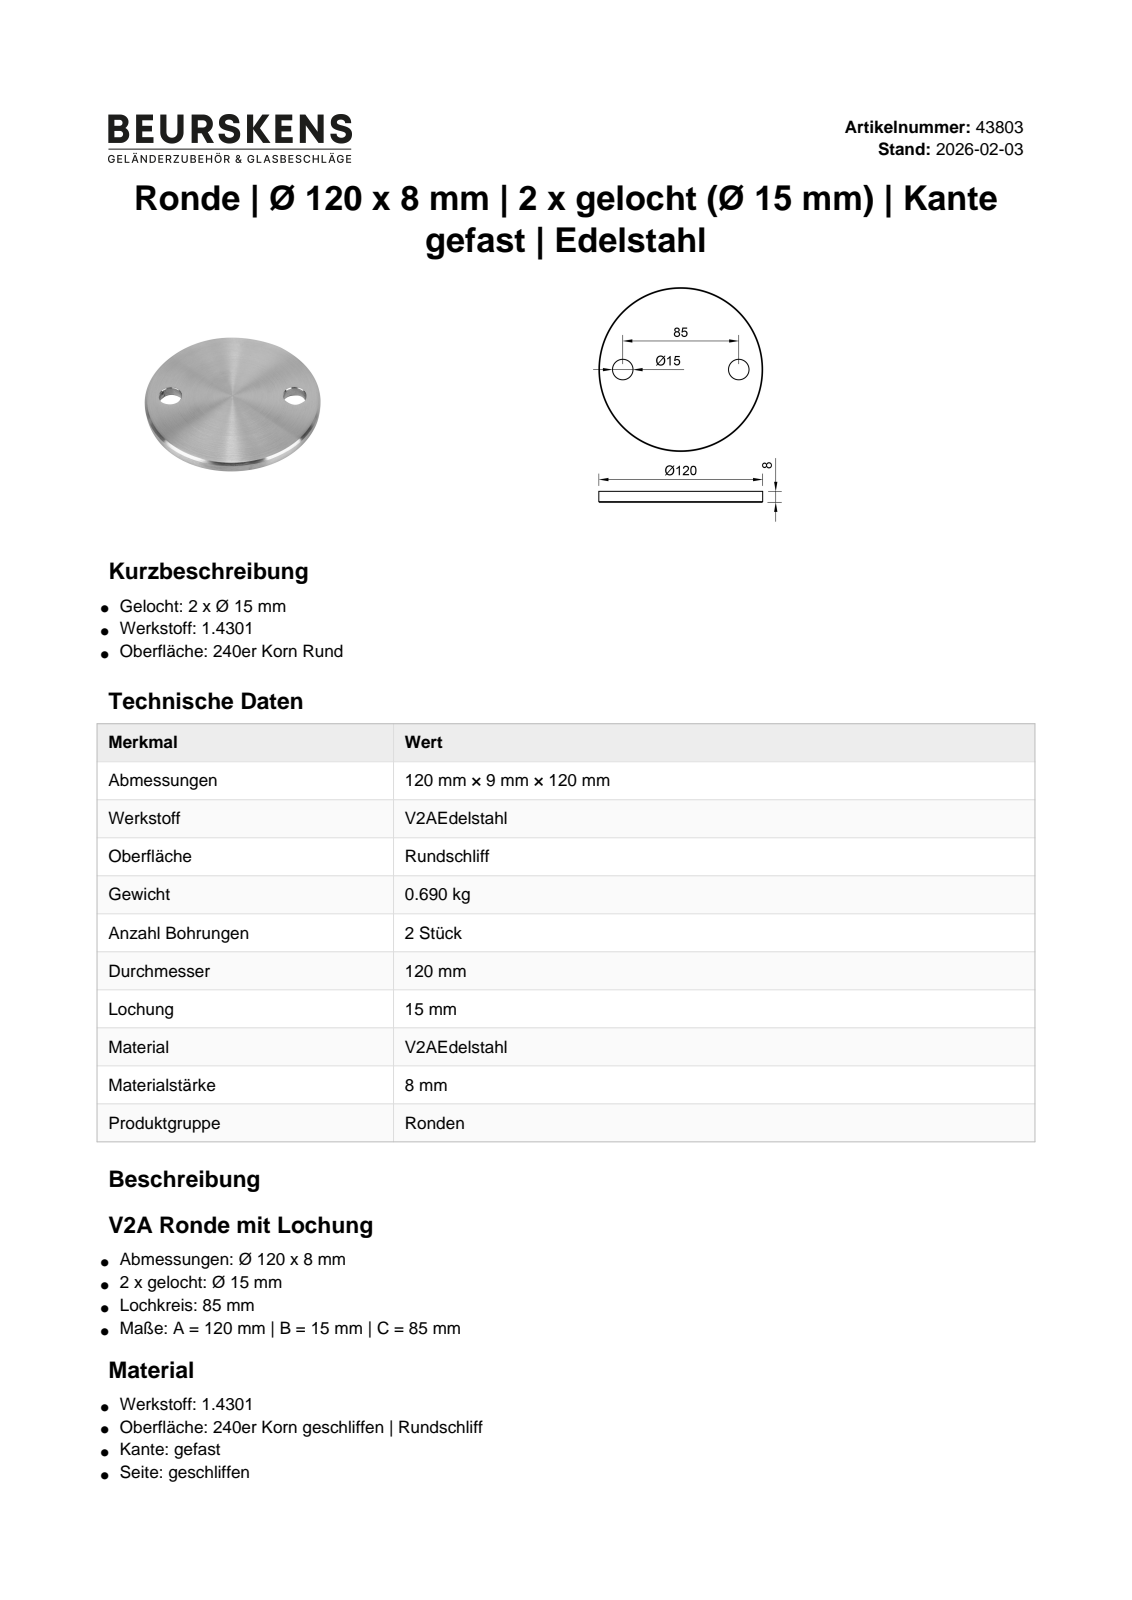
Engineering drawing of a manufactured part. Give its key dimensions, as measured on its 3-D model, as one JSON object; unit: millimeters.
{"part_name": "43803", "step_written_by": "Autodesk Inventor 2022 (AUTOMOTIVE_DESIGN)", "units": "millimeters", "bodies": {"solids": 1, "faces": 6, "planar": 2, "cylindrical": 3, "other": 1}, "overall_size": [120, 120, 8], "volume_mm3": 87603, "surface_area_mm2": 25572, "round_holes": [[15, 2]], "round_bosses_or_shafts": [[120, 1]], "face_to_face_distances": [8], "hole_center_spacings": [85]}
